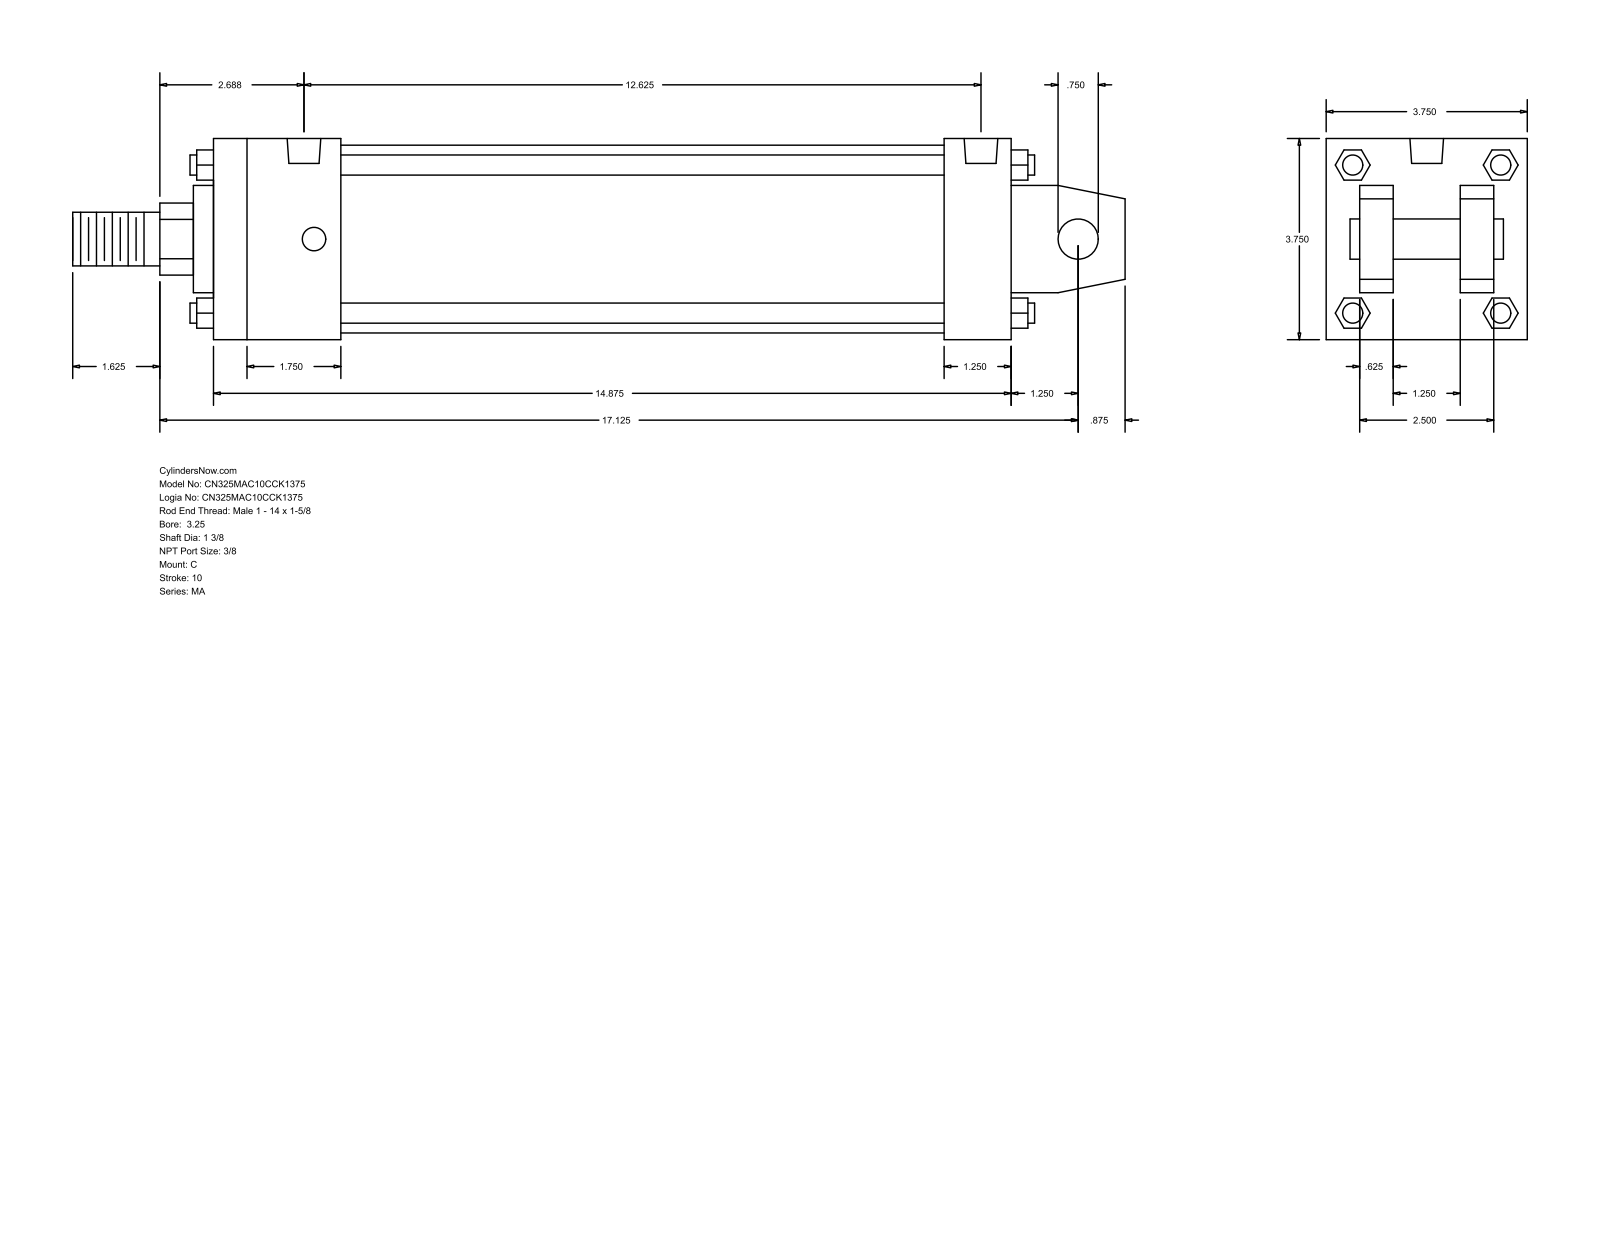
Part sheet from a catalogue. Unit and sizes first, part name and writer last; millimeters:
Units: millimetres
Overall size (bounding box): 498.48 × 95.25 × 95.25
Round holes (diameter × count): ⌀11.11 ×4, ⌀15.93 ×2
Round bosses / shafts (diameter × count): ⌀9.53 ×4, ⌀88.9 ×1, ⌀50.8 ×1, ⌀34.92 ×1, ⌀25.4 ×1, ⌀19.05 ×1
Partial cylindrical surfaces — rounded edges, fillets, slot ends (radius × count): R17.06 ×1
Main face-to-face distances: 95.24, 15.87, 63.5, 377.83, 31.74, 79.37, 47.63, 346.08, 31.75, 60.32
Hole centre spacings: 311.15, 4.76, 4.77, 315.91, 315.92, 320.68
Bodies: 0 solids, 139 faces (108 planar, 31 cylindrical, 0 other)
Part name (STEP PRODUCT): MA_C__0325_1.375
STEP written by: GSSL Pune (CONFIG_CONTROL_DESIGN)
